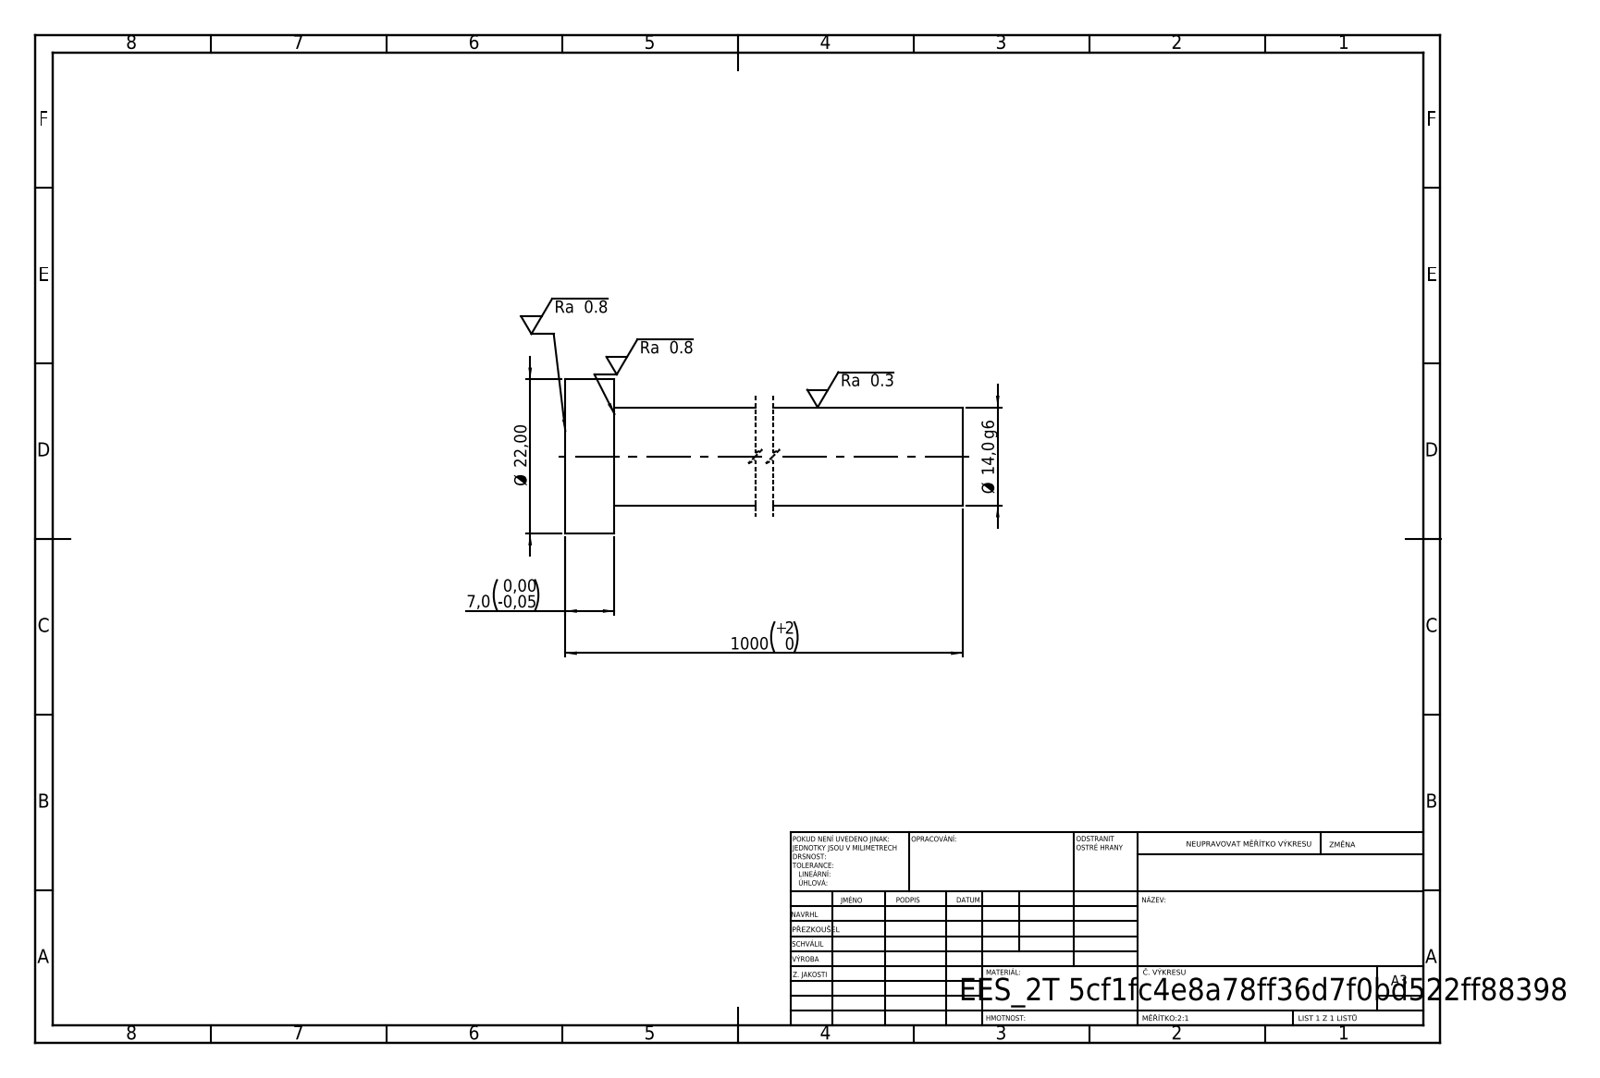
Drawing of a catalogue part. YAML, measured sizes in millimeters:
step_written_by: "SolidWorks 2019 (CONFIG_CONTROL_DESIGN)"
units: millimeters
bodies: {solids: 1, faces: 7, planar: 3, cylindrical: 4, other: 0}
overall_size: [1000, 22, 22]
volume: 155521
surface_area: 44918
round_bosses_or_shafts:
  - {diameter: 22, count: 1}
  - {diameter: 14, count: 1}
face_to_face_distances: [7, 1000, 993]
